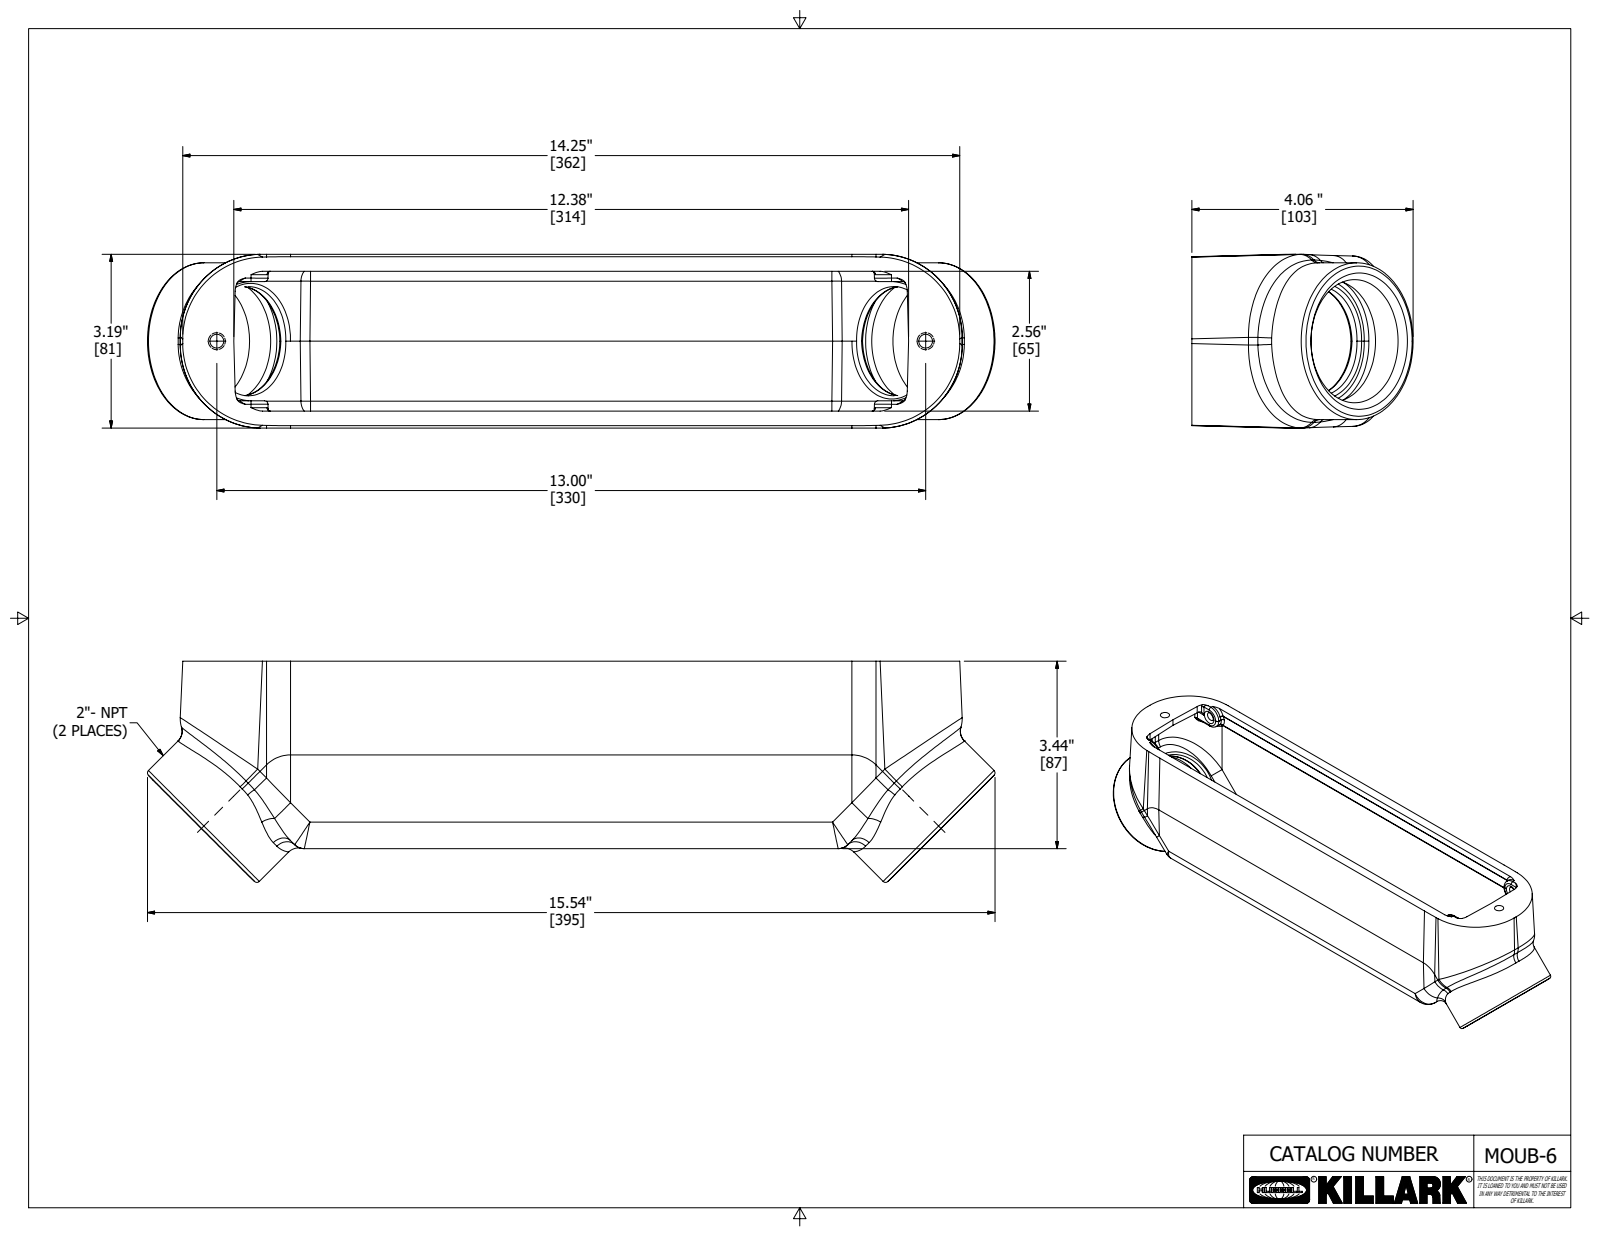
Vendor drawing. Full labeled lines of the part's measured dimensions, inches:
Part name (STEP PRODUCT): 21341-2
STEP written by: Autodesk Inventor 2020 (AUTOMOTIVE_DESIGN)
Units: inches
Bodies: 1 solid, 734 faces (291 planar, 100 cylindrical, 343 other)
Overall size (bounding box): 15.544 × 4.056 × 3.188
Volume: 35.63 in³ · Surface area: 293.4 in²
Round holes (diameter × count): ⌀0.252 ×2, ⌀2.004 ×2, ⌀2.381 ×2
Round bosses / shafts (diameter × count): ⌀2.875 ×2
Partial cylindrical surfaces — rounded edges, fillets, slot ends (radius × count): R0.062 ×20, R0.25 ×16, R0.5 ×16, R0.125 ×10, R0.313 ×8, R0.375 ×4, R1.25 ×4, R1.5 ×4
Main face-to-face distances: 3.187, 2.687, 3.438, 0.031, 0.063, 2.625, 3.406, 2.562, 3, 2.656
Hole centre spacings: 13
